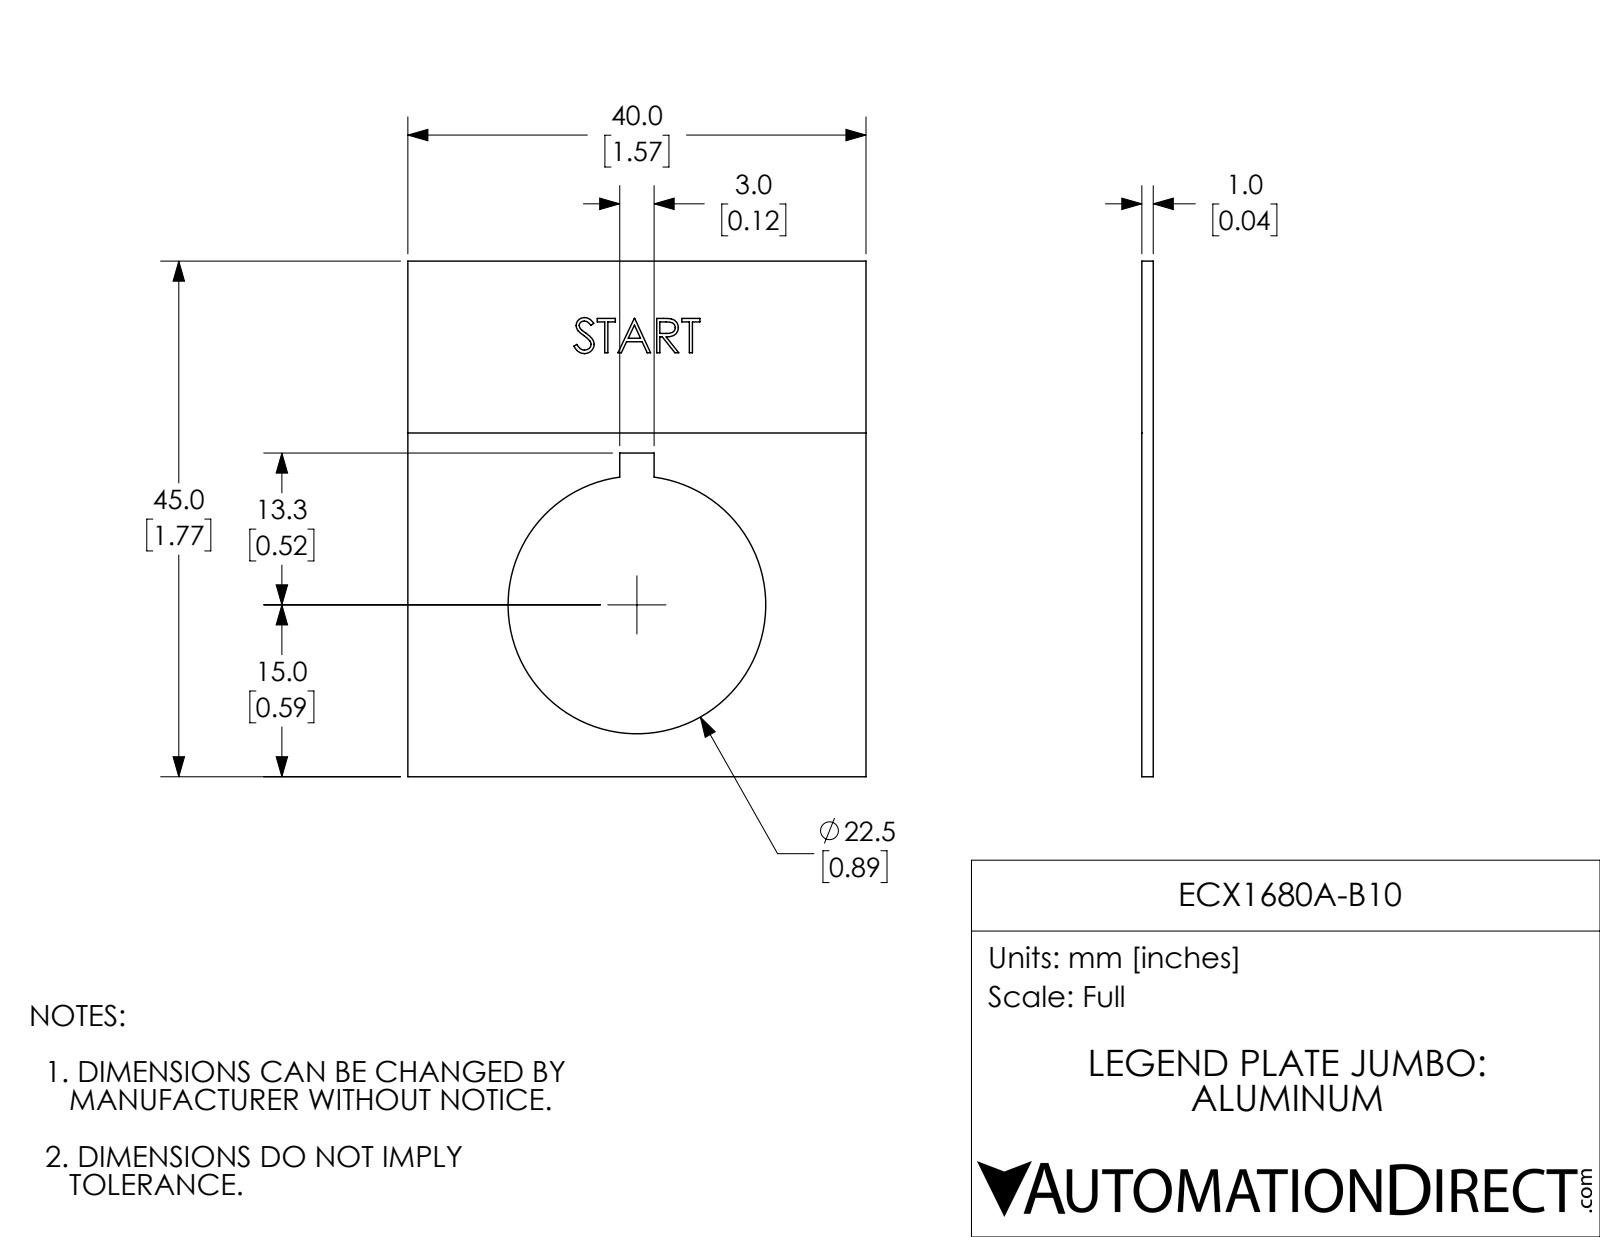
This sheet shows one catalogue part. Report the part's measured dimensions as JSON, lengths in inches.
{"part_name": "ECX1680A-B10", "step_written_by": "SolidWorks 2017 (AUTOMOTIVE_DESIGN)", "units": "inches", "bodies": {"solids": 1, "faces": 81, "planar": 58, "cylindrical": 3, "other": 20}, "overall_size": [1.772, 1.575, 0.039], "volume_in3": 0.085, "surface_area_in2": 4.709, "round_holes": [[0.886, 1]], "face_to_face_distances": [0.039, 0.039, 1.575, 1.772, 0.728, 0.846, 1.112, 0.659, 0.118, 1.181]}
